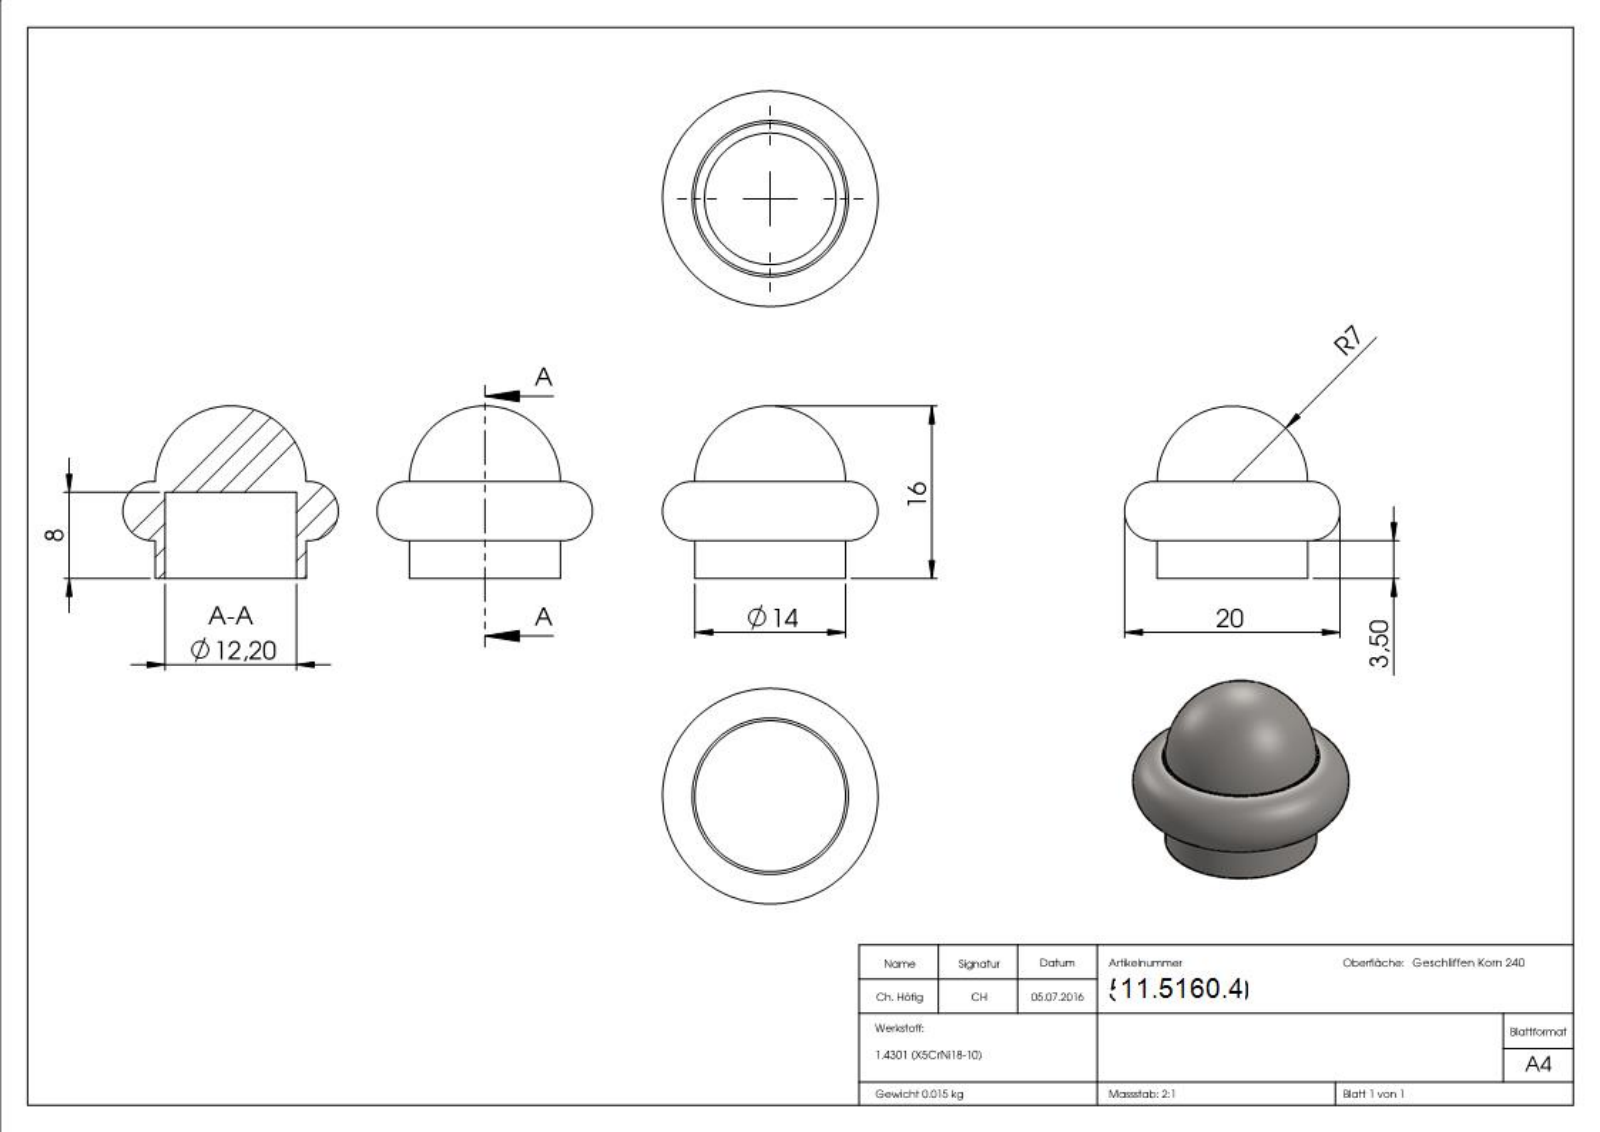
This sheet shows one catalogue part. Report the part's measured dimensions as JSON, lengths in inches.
{"part_name": "51016-240", "step_written_by": "SolidWorks 2015 (CONFIG_CONTROL_DESIGN)", "units": "inches", "bodies": {"solids": 1, "faces": 223, "planar": 126, "cylindrical": 4, "other": 93}, "overall_size": [0.787, 0.787, 0.63], "volume_in3": 0.113, "surface_area_in2": 2.265, "round_holes": [[0.48, 1]], "round_bosses_or_shafts": [[0.551, 1]], "face_to_face_distances": [0.315, 0.354, 0.039, 0.138, 0.177, 0.217, 0.02, 0.335, 0.197, 0.033]}
